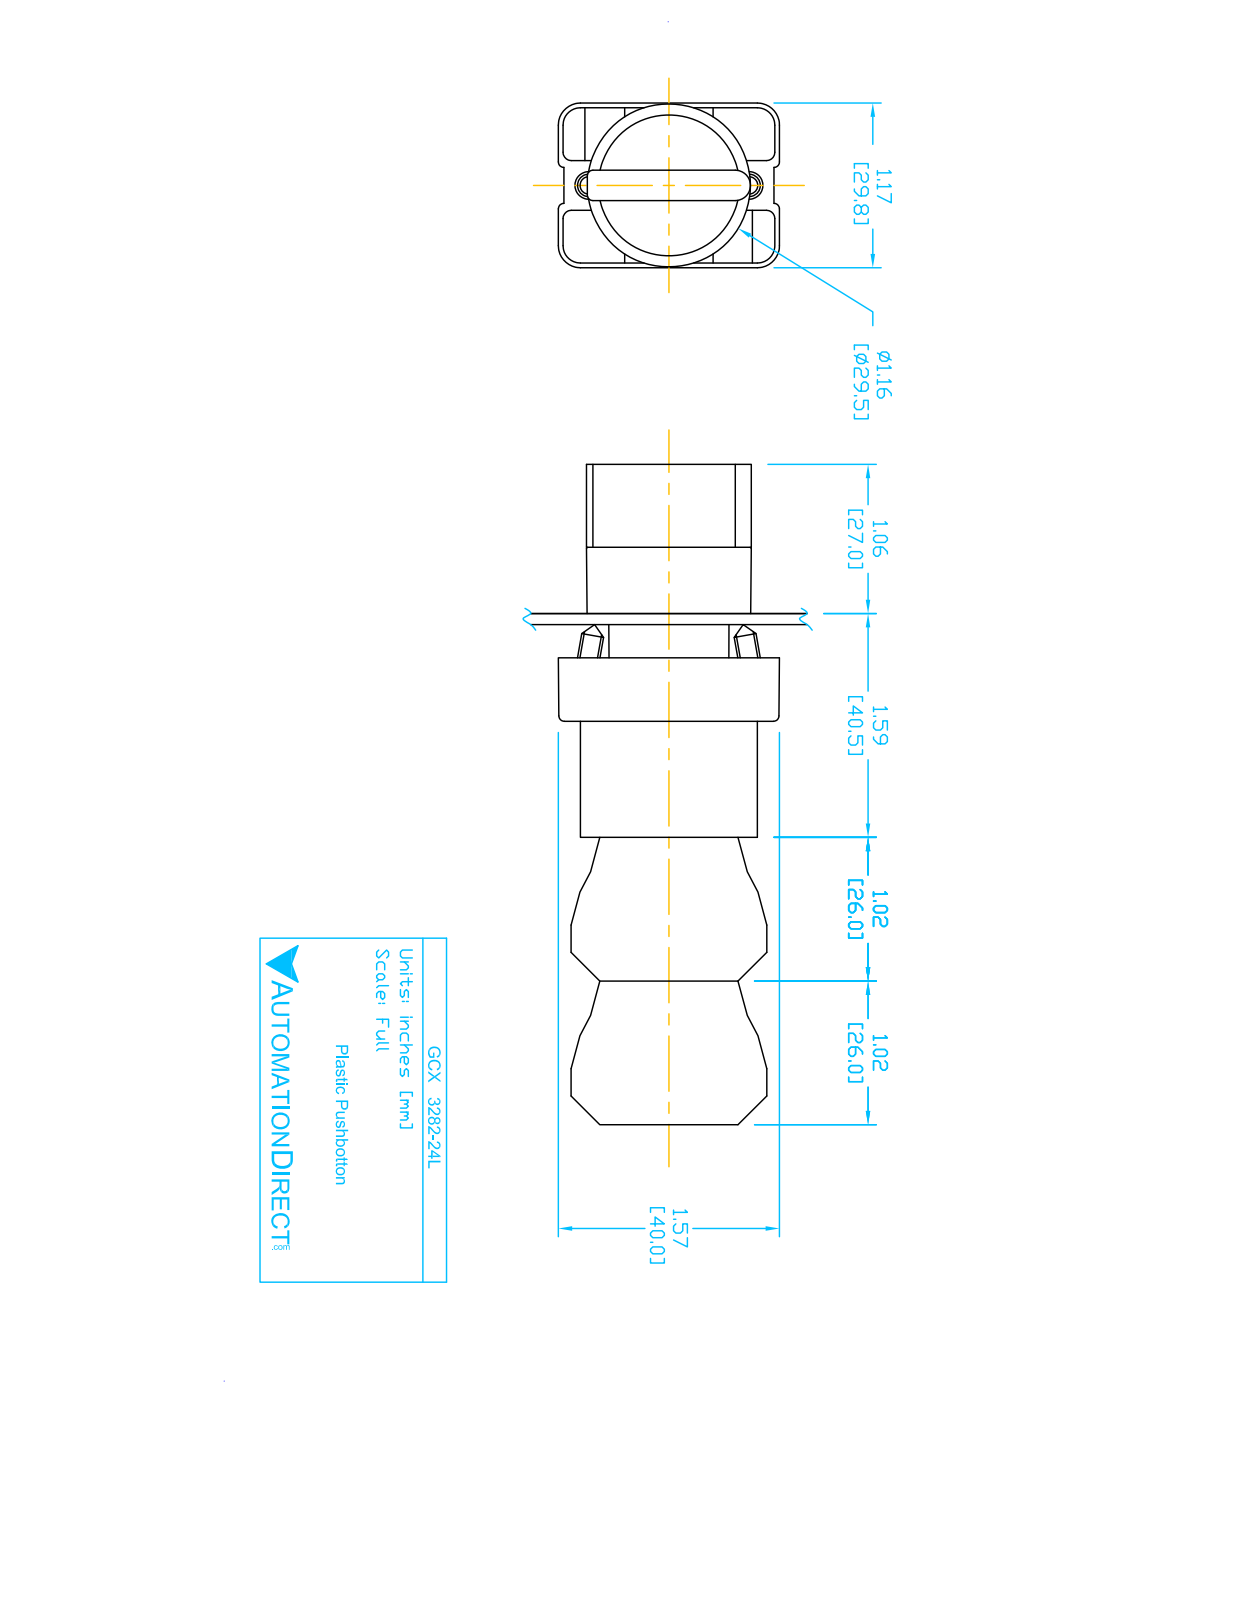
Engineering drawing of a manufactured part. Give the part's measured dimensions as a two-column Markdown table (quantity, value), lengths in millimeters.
| quantity | value |
| --- | --- |
| part name | ECX1050; ECX3029-2; ecx1040; GCX3282-24L (+2 more) |
| STEP written by | SolidWorks 2016 (AUTOMOTIVE_DESIGN) |
| units | millimeters |
| bodies | 11 solids, 724 faces (488 planar, 193 cylindrical, 43 other) |
| overall size | 118.8 × 40.2 × 29.9 |
| volume | 77 850 mm³ |
| surface area | 38 210 mm² |
| round holes (diameter × count) | 2 × 4, 2.2 × 2, 3.1 × 2, 3.3 × 2, 5 × 1, 11.9 × 1, 22.3 × 1, 22.6 × 1, 26 × 1 |
| round bosses / shafts (diameter × count) | 4 × 4, 29.8 × 1, 25.5 × 1, 24 × 1, 21.7 × 1, 19.8 × 1, 12.8 × 1 |
| partial cylindrical surfaces (radius × count) | 1.5 × 24, 1 × 12, 3.1 × 12, 4 × 12, 1 × 9, 0.5 × 2, 1.6 × 2, 2 × 2 |
| main face-to-face distances | 14.7, 15.1, 26, 29.7, 0.4, 21, 47, 77.3, 51.3, 30.3 |
| hole center spacings | 6, 25.5, 24.7, 12, 13.7, 13.8, 27.5, 12.3 |
